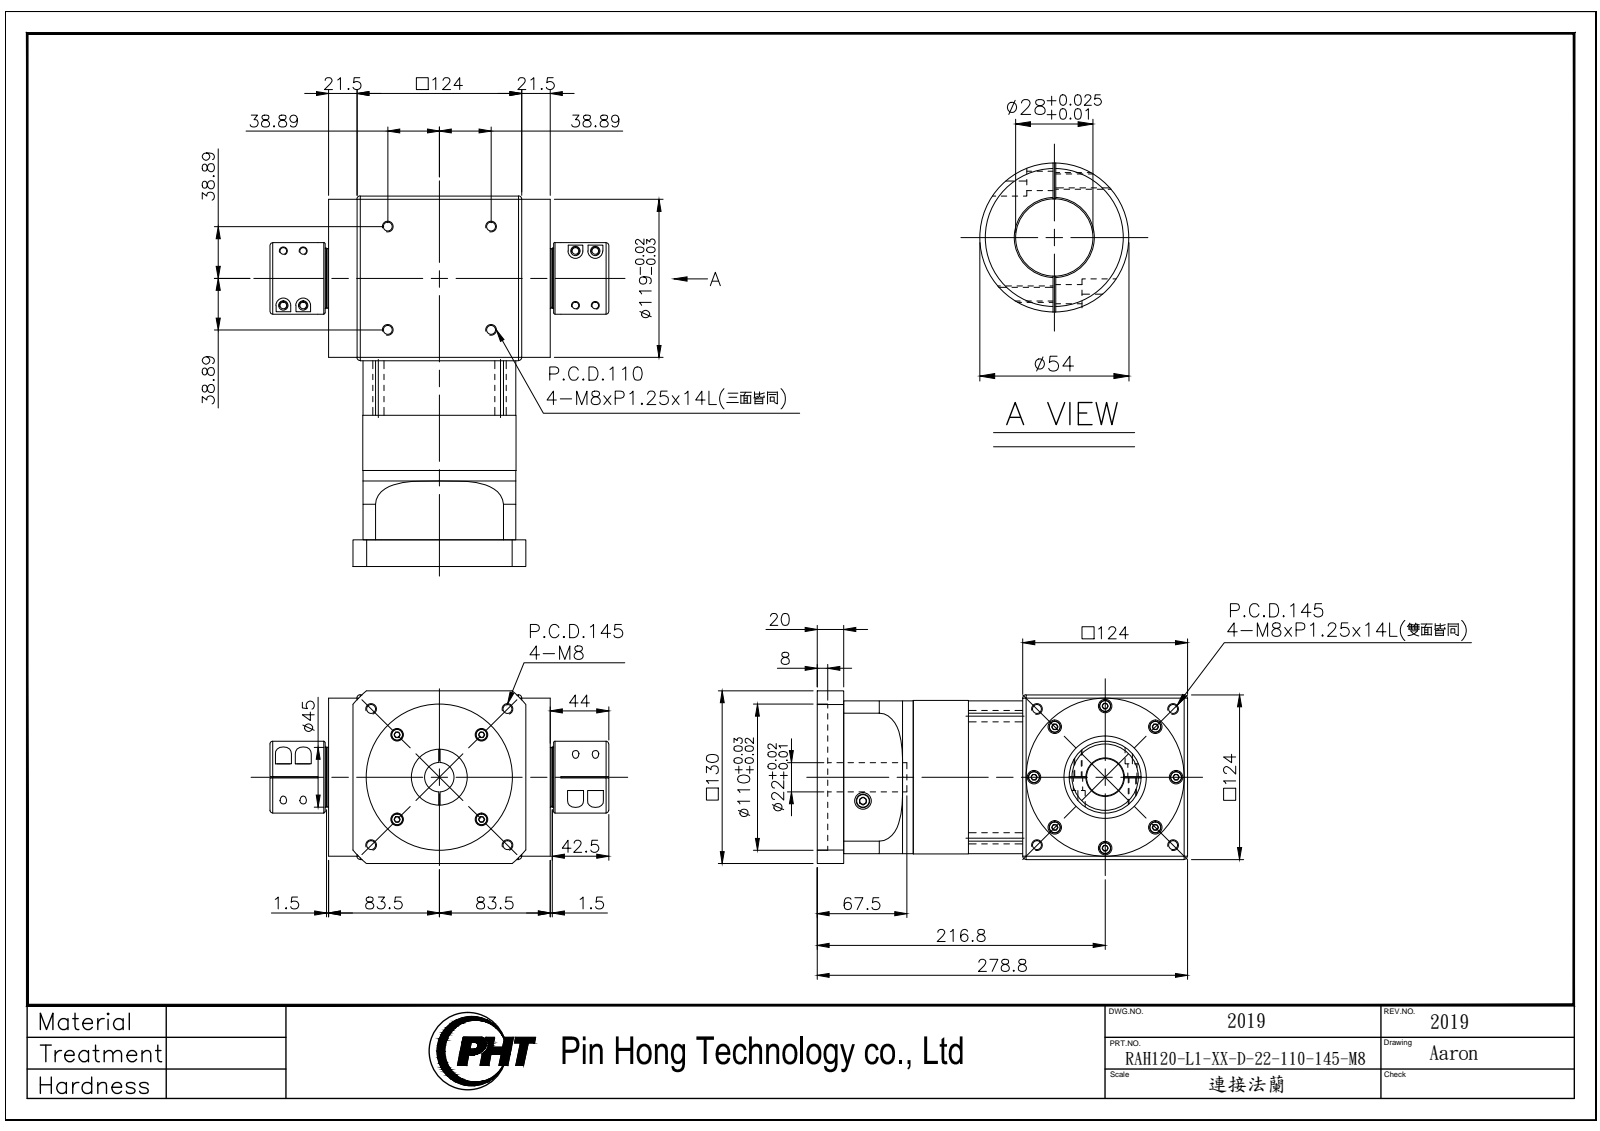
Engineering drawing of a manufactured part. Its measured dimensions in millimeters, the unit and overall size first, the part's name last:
Units: millimetres
Overall size (bounding box): 278.8 × 255 × 130
Round holes (diameter × count): ⌀6.8 ×16, ⌀9.5 ×12, ⌀5.4 ×8, ⌀7 ×8, ⌀9 ×8, ⌀14 ×8, ⌀5 ×4, ⌀5.5 ×4, ⌀8.5 ×4, ⌀12.7 ×2, ⌀22 ×1, ⌀28 ×1
Round bosses / shafts (diameter × count): ⌀13 ×12, ⌀10.5 ×8, ⌀10 ×8, ⌀6 ×8, ⌀8.5 ×4, ⌀119 ×1, ⌀115.5 ×1, ⌀115 ×1
Partial cylindrical surfaces — rounded edges, fillets, slot ends (radius × count): R3.52 ×8, R5.5 ×8, R75 ×1, R85 ×1, R86.2 ×1
Main face-to-face distances: 124, 4.5, 119.5, 3, 115, 26, 141, 127, 121, 7.5
Hole centre spacings: 54, 10, 14.26, 15.71, 18.98, 24.68, 39.8, 51.28
Volume: 4 117 000 mm³ · Surface area: 347 266 mm²
Bodies: 2 solids, 1275 faces (643 planar, 408 cylindrical, 224 other)
Part name (STEP PRODUCT): RAH120-L1-XX-D-22-110-145-M8_2019
STEP written by: SolidWorks 2016 (AUTOMOTIVE_DESIGN)
